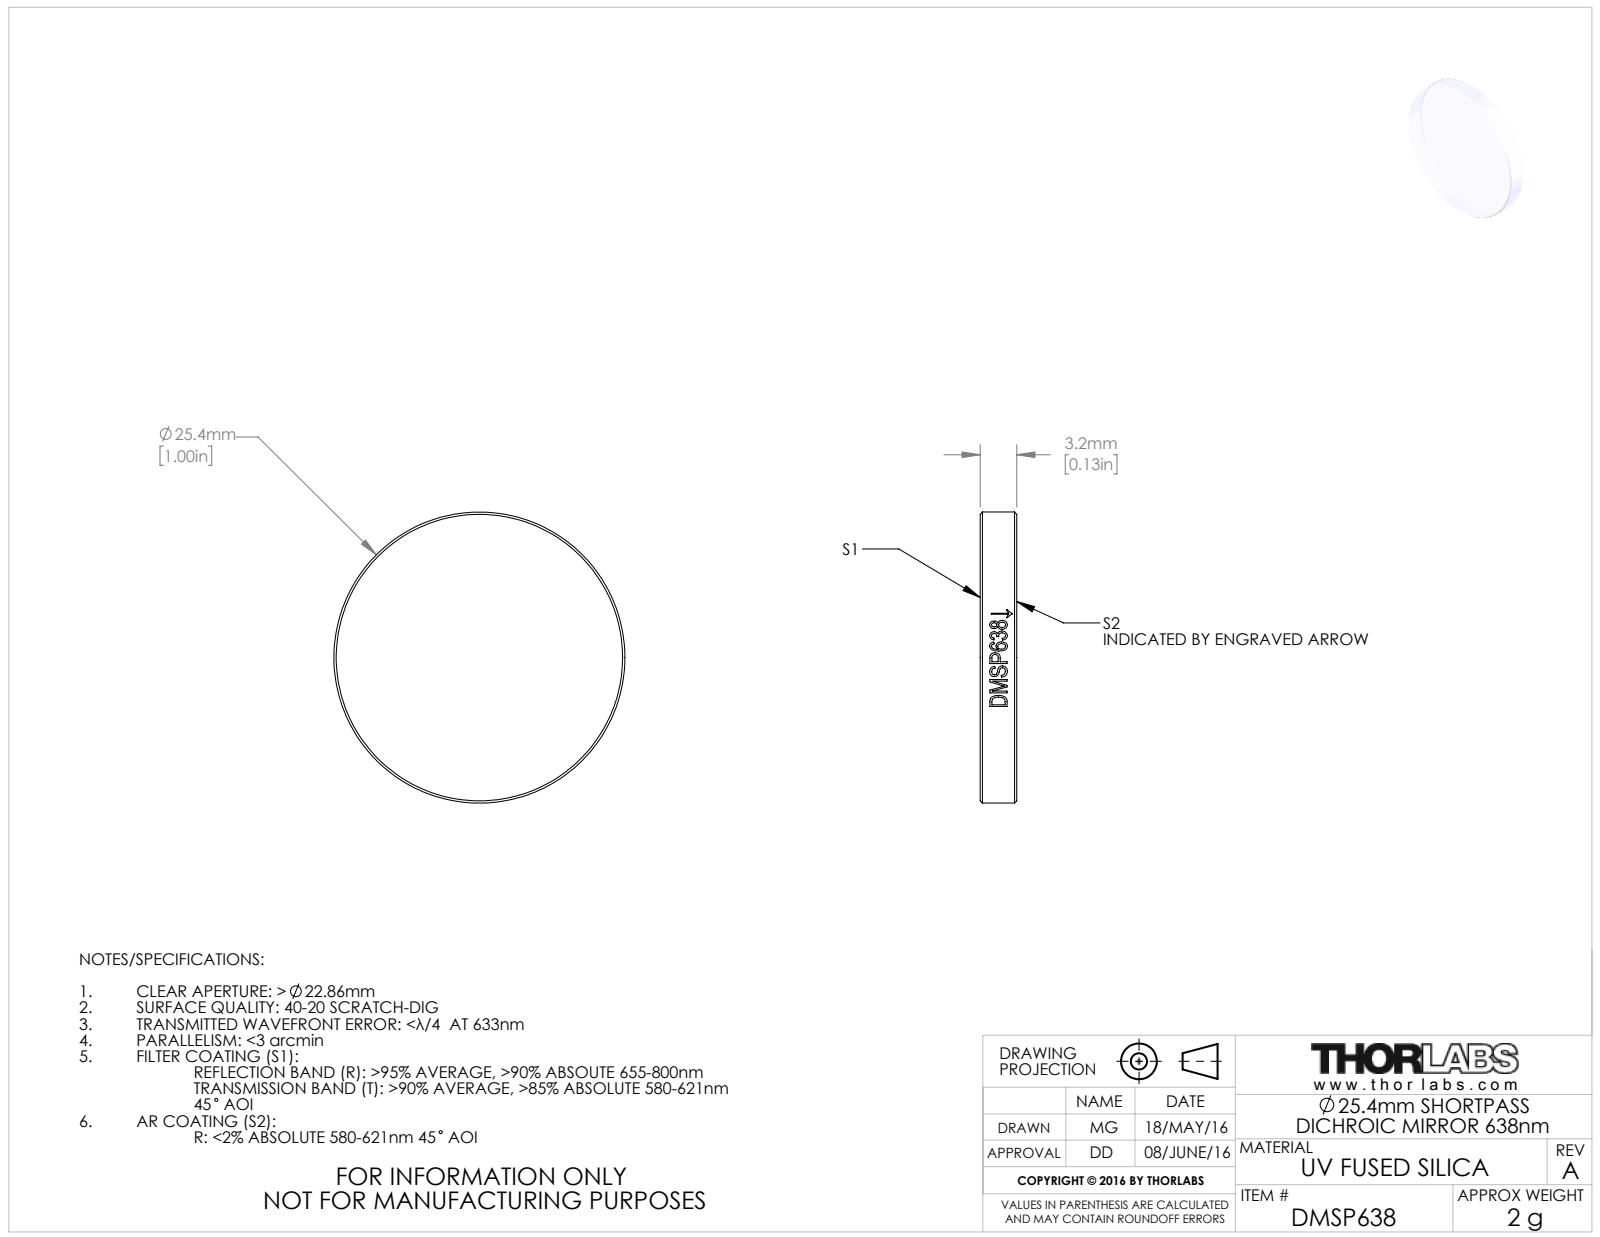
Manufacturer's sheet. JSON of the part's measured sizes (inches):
{"part_name": "TTN045153-E0W", "step_written_by": "SolidWorks 2016 (CONFIG_CONTROL_DESIGN)", "units": "inches", "bodies": {"solids": 1, "faces": 21, "planar": 2, "cylindrical": 15, "other": 4}, "overall_size": [1, 1, 0.126], "volume_in3": 0.099, "surface_area_in2": 1.938, "round_bosses_or_shafts": [[1, 1]], "face_to_face_distances": [0.126]}
